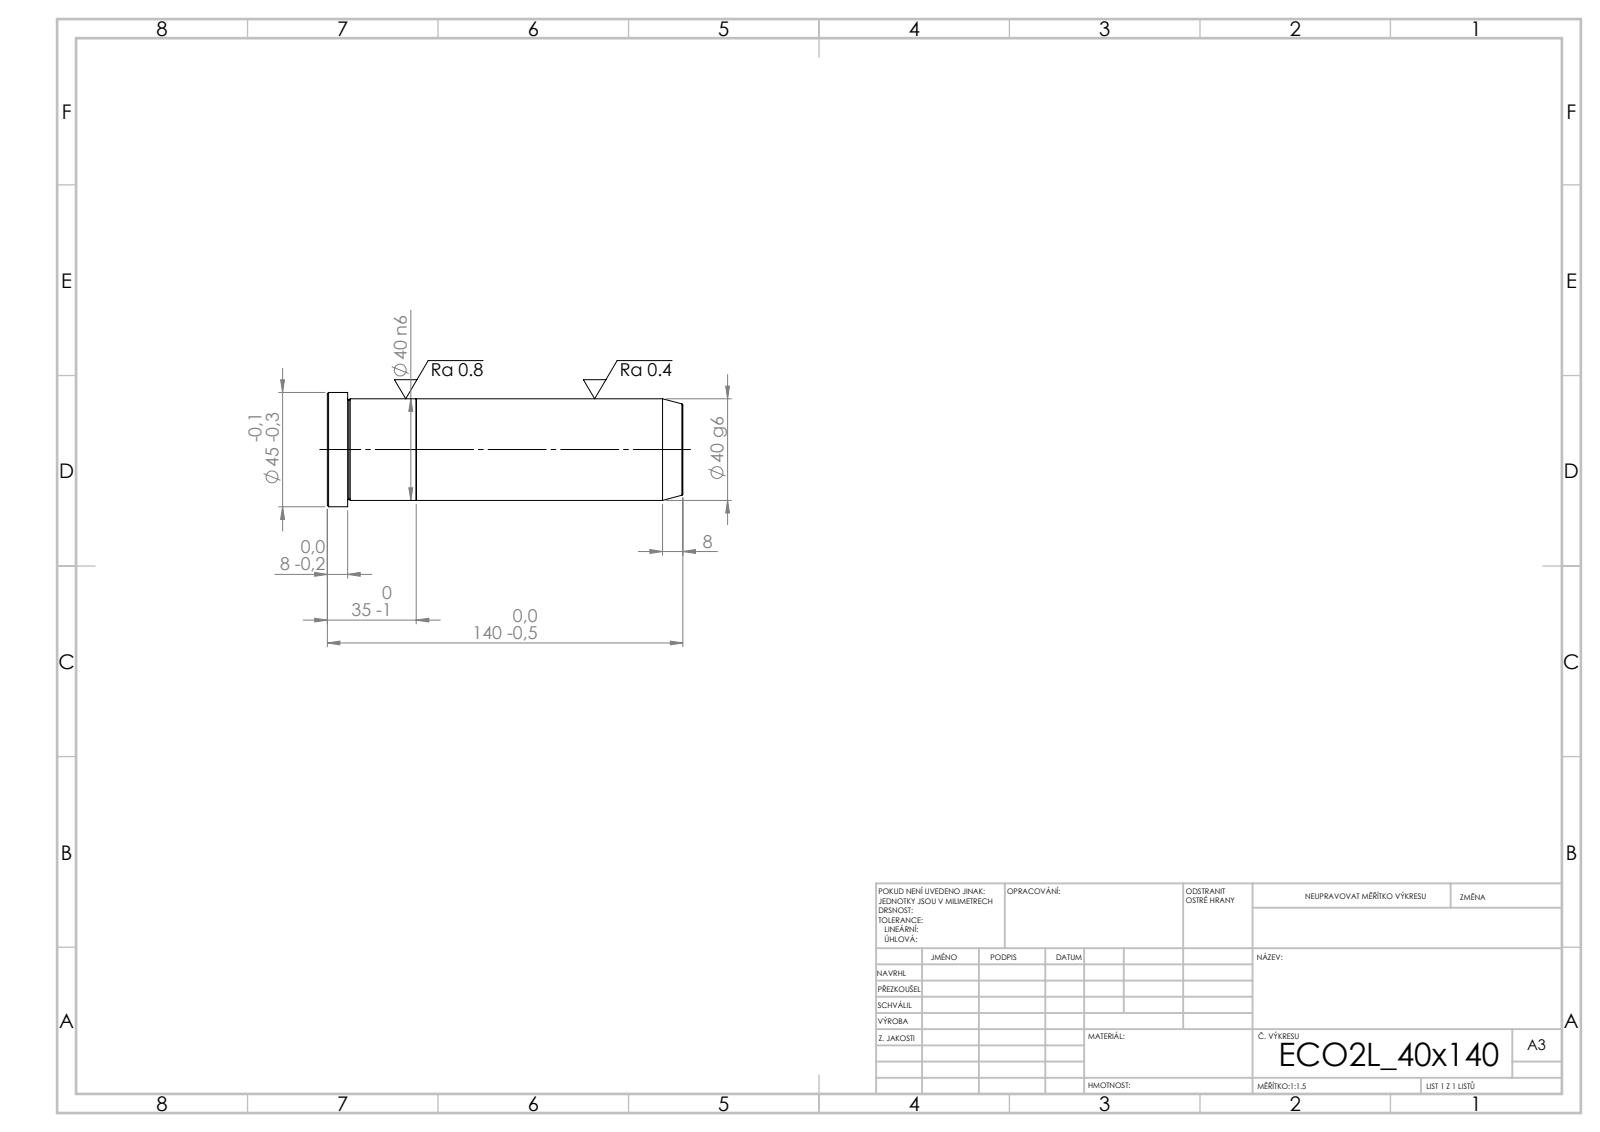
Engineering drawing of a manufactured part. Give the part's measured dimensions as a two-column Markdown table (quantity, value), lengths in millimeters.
| quantity | value |
| --- | --- |
| STEP written by | SolidWorks 2019 (CONFIG_CONTROL_DESIGN) |
| units | millimeters |
| bodies | 2 solids, 21 faces (5 planar, 6 cylindrical, 10 other) |
| overall size | 140 × 45 × 45 |
| volume | 177 491 mm³ |
| surface area | 23 152 mm² |
| round bosses / shafts (diameter × count) | 45 × 1, 40 × 1 |
| main face-to-face distances | 35, 105, 140, 132, 27, 8 |
